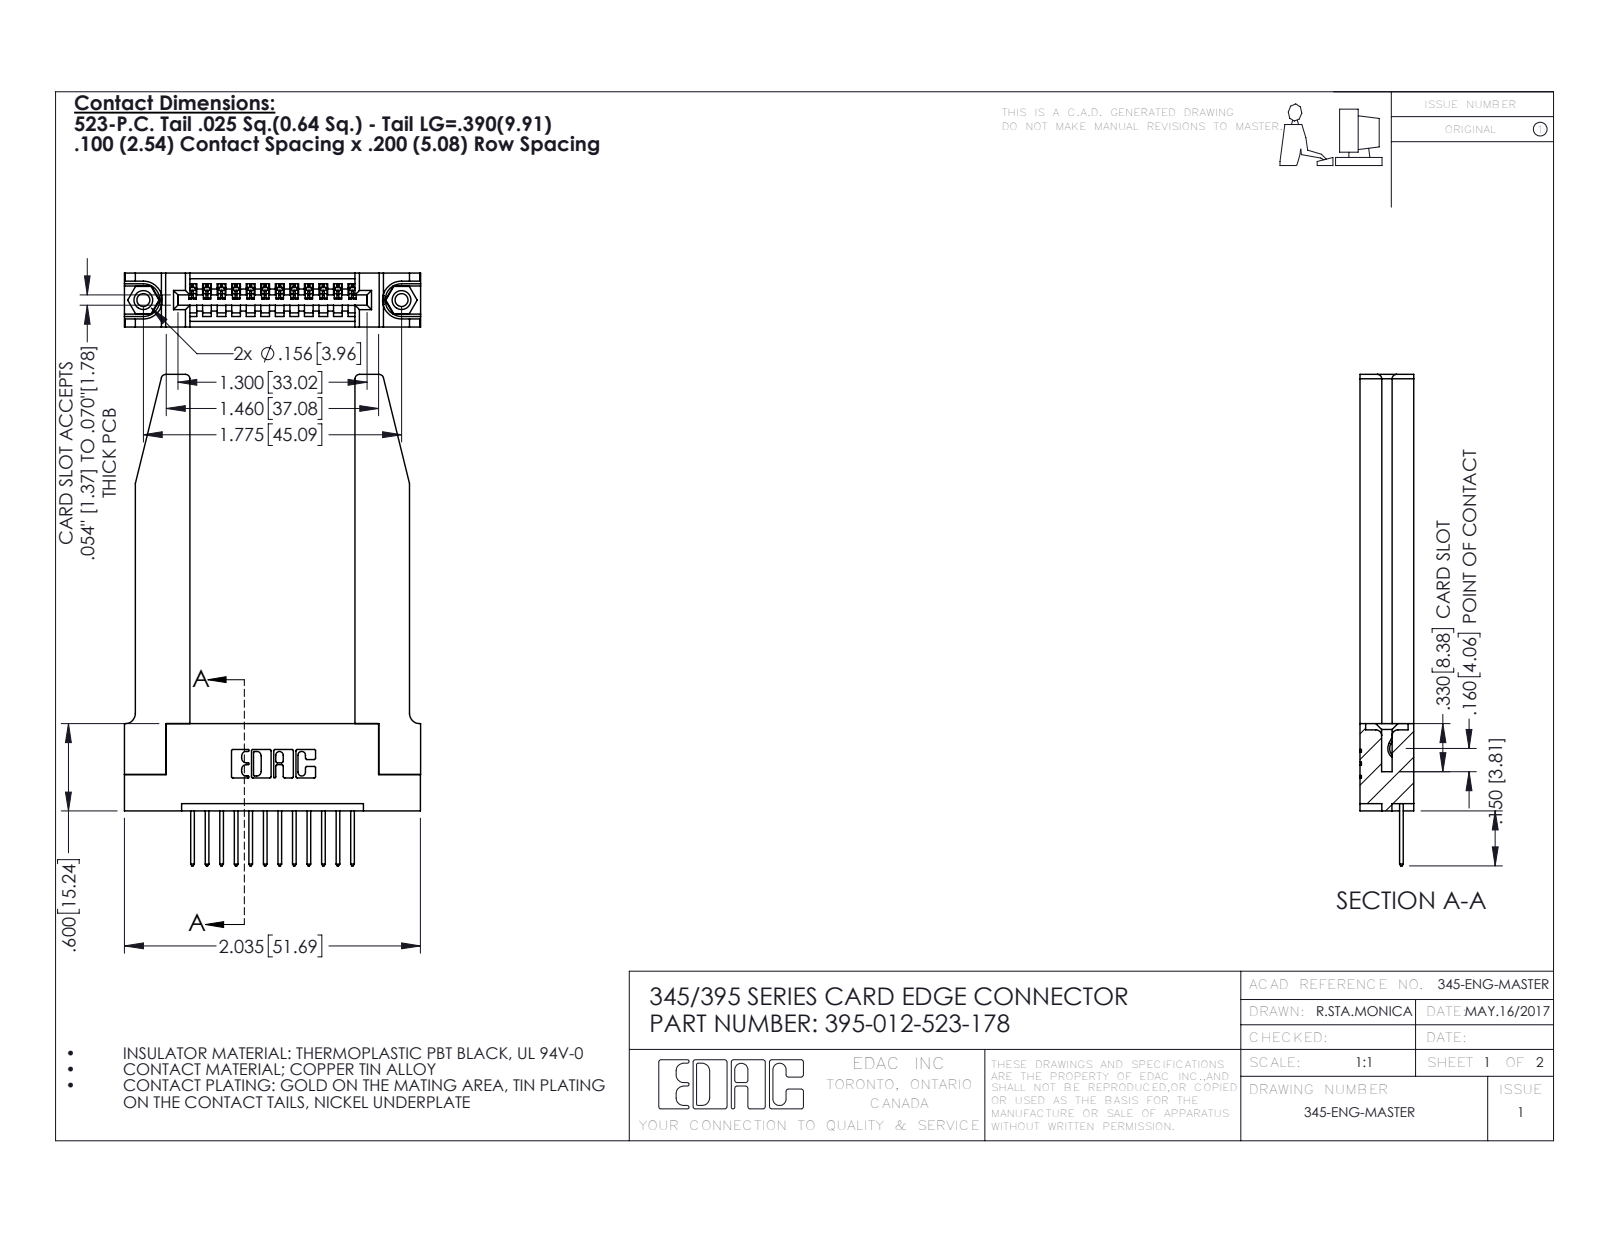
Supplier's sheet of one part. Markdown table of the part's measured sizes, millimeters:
| quantity | value |
| --- | --- |
| part name | 345 Part_Flush Mounting Lugs - 0.156 Dia-TH; 345-220-078_345-220-078; 345-292-001_345-293-123; 395-012-523-178 (+1 more) |
| STEP written by | SolidWorks 2016 (CONFIG_CONTROL_DESIGN) |
| units | millimeters |
| bodies | 17 solids, 1056 faces (702 planar, 302 cylindrical, 52 other) |
| overall size | 85.8 × 51.7 × 9.4 |
| volume | 12 400 mm³ |
| surface area | 12 650 mm² |
| round holes (diameter × count) | 2.3 × 2, 3.2 × 2, 4 × 2, 1.6 × 1 |
| round bosses / shafts (diameter × count) | 3.9 × 2 |
| partial cylindrical surfaces (radius × count) | 0.2 × 24, 0.3 × 24, 0.3 × 22, 0.8 × 8, 0.2 × 6, 0.8 × 6, 0.7 × 3, 0.8 × 2 |
| main face-to-face distances | 9.4, 1.8, 7.6, 5.1, 3.8, 3.8, 2, 5.6, 28.8, 2.5 |
| hole center spacings | 6.9, 39.2, 45.1 |
